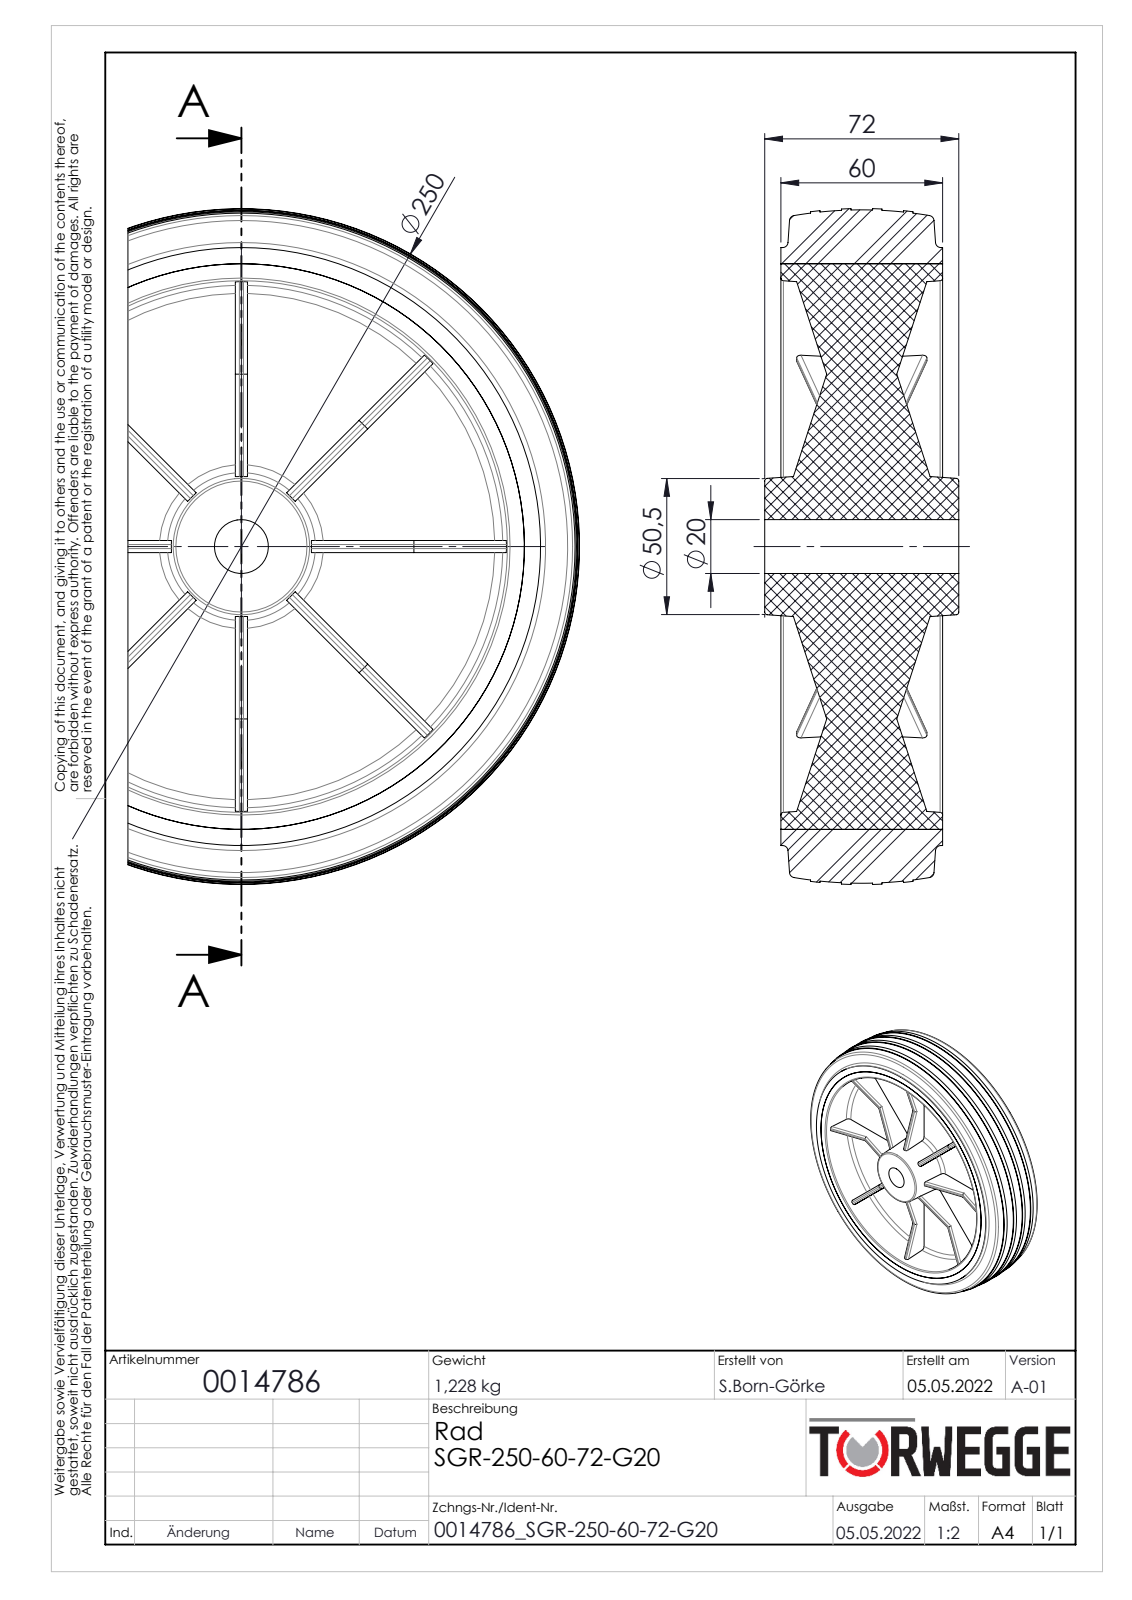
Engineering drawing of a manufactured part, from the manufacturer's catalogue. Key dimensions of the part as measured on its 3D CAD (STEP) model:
Part name (STEP PRODUCT): 0014786
STEP written by: SolidWorks 2020 (AUTOMOTIVE_DESIGN)
Units: millimetres
Bodies: 2 solids, 246 faces (94 planar, 74 cylindrical, 78 other)
Overall size (bounding box): 250.89 × 250.89 × 72
Volume: 1 388 000 mm³ · Surface area: 298 502 mm²
Round holes (diameter × count): ⌀20 ×1, ⌀210 ×1
Round bosses / shafts (diameter × count): ⌀222 ×1
Partial cylindrical surfaces — rounded edges, fillets, slot ends (radius × count): R1.5 ×64
Main face-to-face distances: 4, 4.5, 32, 28, 60, 6, 34, 38, 66, 11.5
